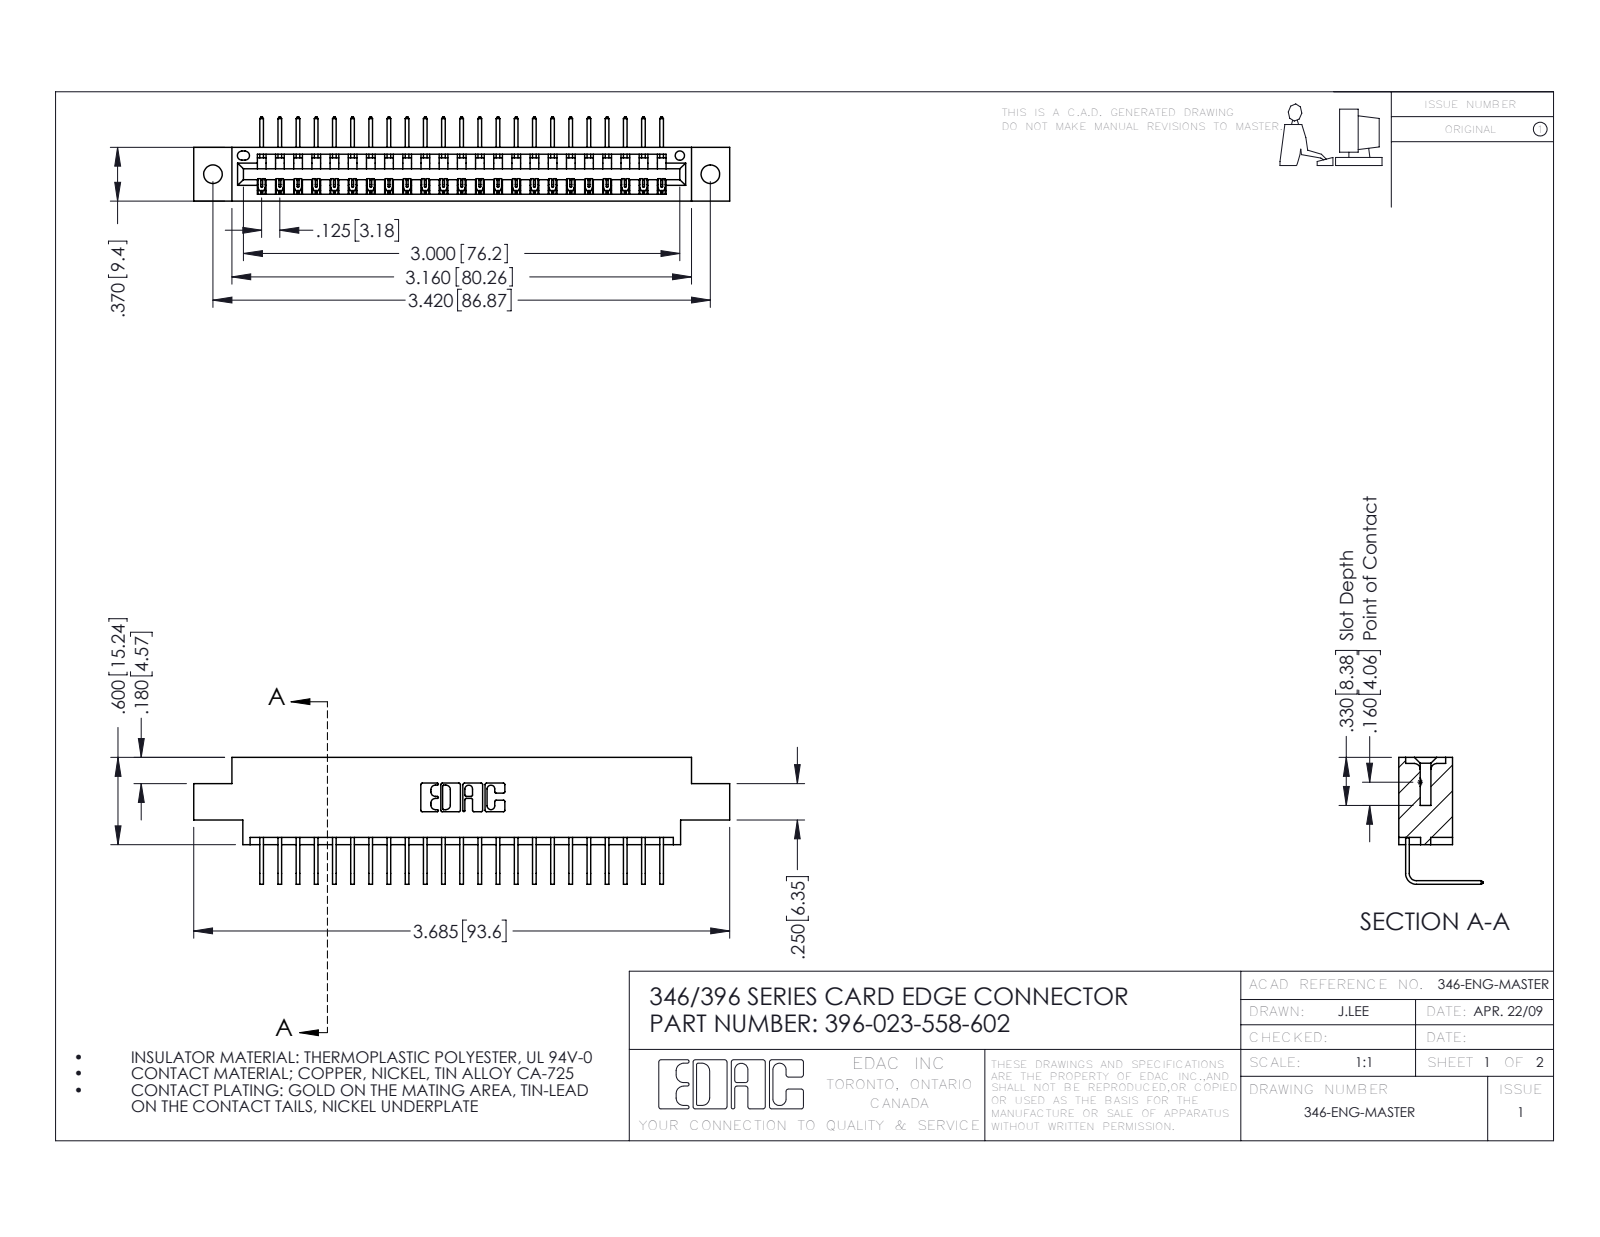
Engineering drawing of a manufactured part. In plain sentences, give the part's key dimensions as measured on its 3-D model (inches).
The part is named "345-292-001_558 Tail - 2; 346 Part_0.170 Offset - 0.128 Dia; 396-023-558-602". Its 3-D file was written by "SolidWorks 2016 (CONFIG_CONTROL_DESIGN)". It is 24 solids with 1506 faces: 1046 planar, 460 cylindrical and 0 other. Overall it measures 3.685 by 0.873 by 0.58 inches. Its volume is 0.532 cubic inches and its surface area 17.1 square inches. Round holes: 2 of diameter 0.128, 1 of diameter 0.064. Partial cylindrical surfaces (rounded edges, fillets, slot ends): 46 of radius 0.006, 22 of radius 0.01, 6 of radius 0.007, 6 of radius 0.031, 3 of radius 0.026, 2 of radius 0.031, 2 of radius 0.04, 1 of radius 0.014. The main face-to-face distances are 0.322, 0.048, 0.37, 0.25, 0.298, 0.025, 0.072, 0.148, 0.222, 0.1. The hole center spacings are 0.246, 3.212, 3.42.
